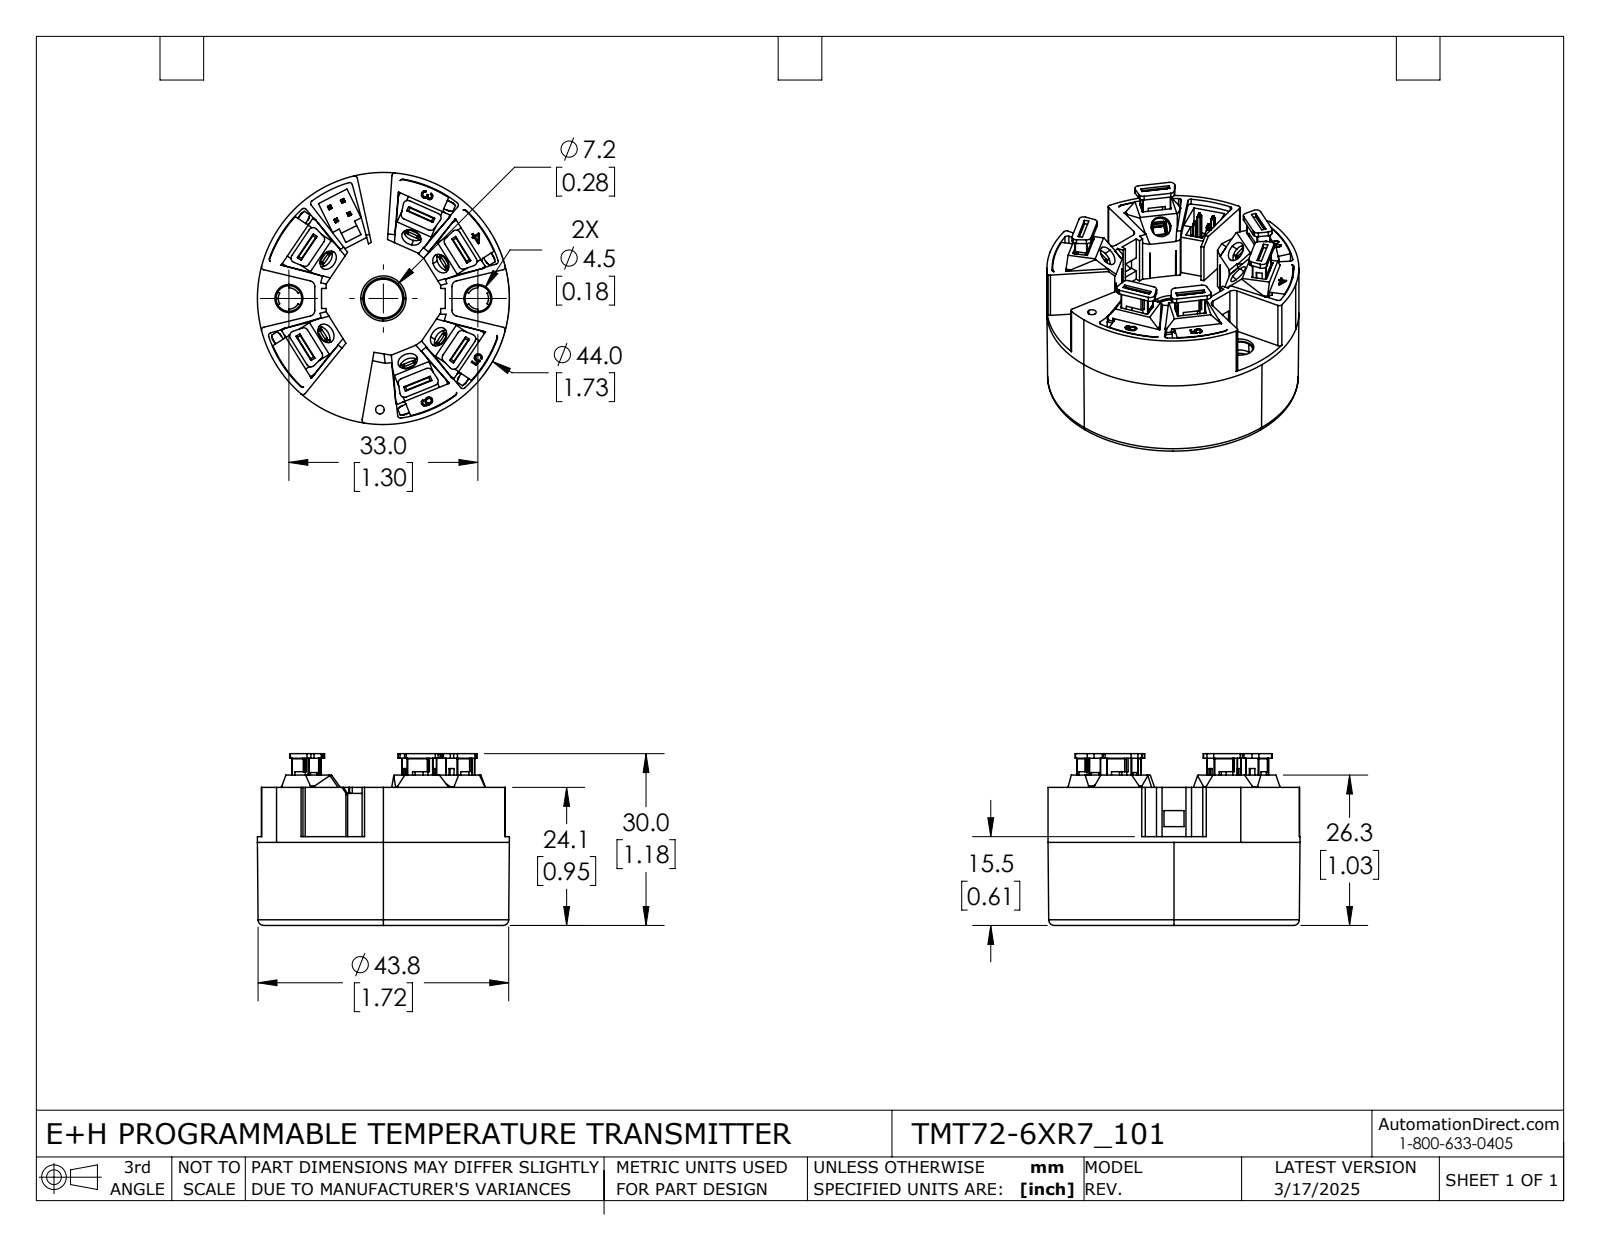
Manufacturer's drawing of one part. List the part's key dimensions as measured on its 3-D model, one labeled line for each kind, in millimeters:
Part name (STEP PRODUCT): TMT72-6XR7_101
STEP written by: SolidWorks 2024 (AUTOMOTIVE_DESIGN)
Units: millimetres
Bodies: 1 solid, 1044 faces (551 planar, 264 cylindrical, 229 other)
Overall size (bounding box): 44 × 44 × 30
Volume: 29 400 mm³ · Surface area: 14 970 mm²
Round holes (diameter × count): ⌀3.5 ×6, ⌀4.9 ×2, ⌀1.5 ×1, ⌀5.4 ×1, ⌀7.2 ×1, ⌀41.8 ×1
Round bosses / shafts (diameter × count): ⌀44 ×1, ⌀41.8 ×1
Partial cylindrical surfaces — rounded edges, fillets, slot ends (radius × count): R0.1 ×73, R0.5 ×34, R0.8 ×24, R0.3 ×22, R0.2 ×12, R1 ×10, R22 ×6, R1.9 ×2
Main face-to-face distances: 1.5, 0.5, 1, 14.5, 14, 15.5, 24.1, 23.1, 22.6, 8.6
Hole centre spacings: 16.5, 7.6, 13.4, 19.4, 21.9, 25.1, 25.9, 26
